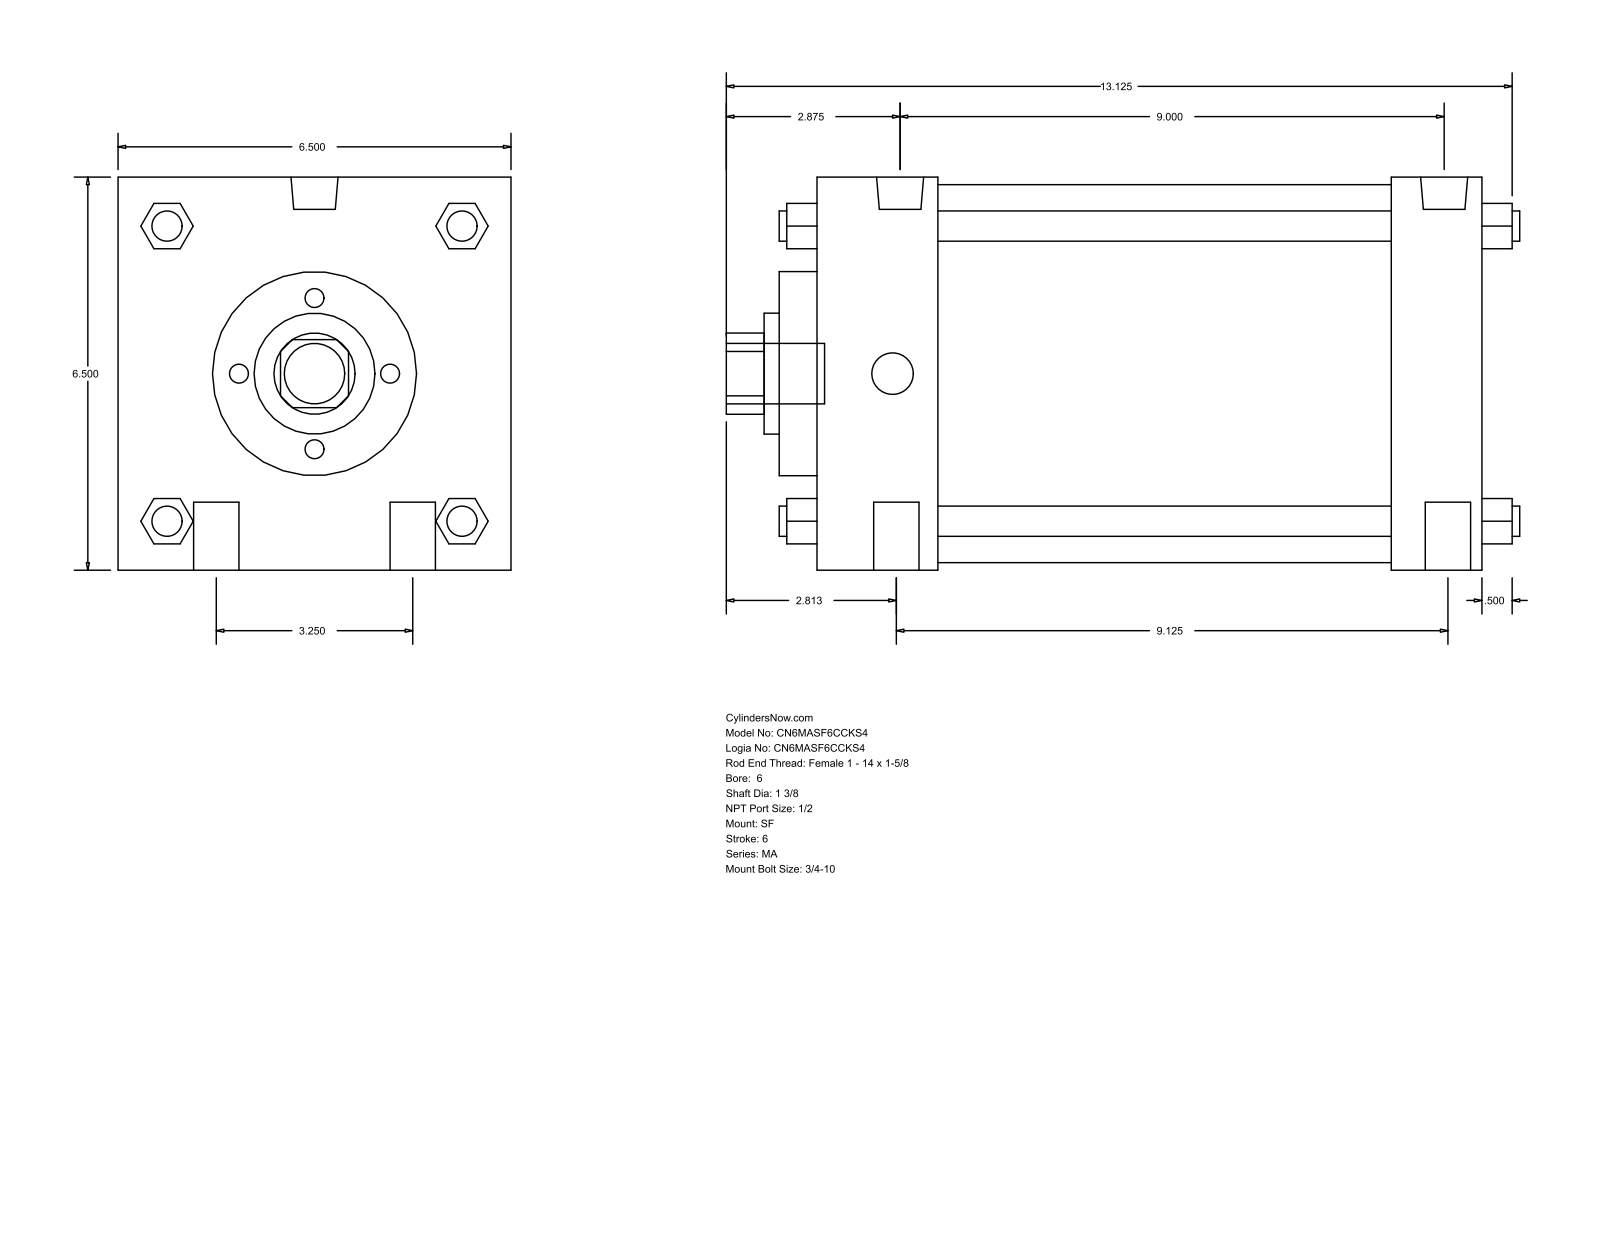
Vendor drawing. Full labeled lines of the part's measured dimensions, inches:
Part name (STEP PRODUCT): MA_SF__0600_1.375
STEP written by: GSSL Pune (CONFIG_CONTROL_DESIGN)
Units: inches
Bodies: 0 solids, 126 faces (95 planar, 31 cylindrical, 0 other)
Overall size (bounding box): 13.125 × 6.5 × 6.5
Round holes (diameter × count): ⌀1.375 ×1, ⌀2 ×1, ⌀3.375 ×1, ⌀6.25 ×1
Round bosses / shafts (diameter × count): ⌀0.75 ×4, ⌀0.5 ×4, ⌀0.778 ×2, ⌀0.687 ×2, ⌀1 ×1
Partial cylindrical surfaces — rounded edges, fillets, slot ends (radius × count): R0.672 ×1
Main face-to-face distances: 6.5, 11, 9.5, 2, 1.5, 7.5, 9, 0.625, 2.625, 10.125
